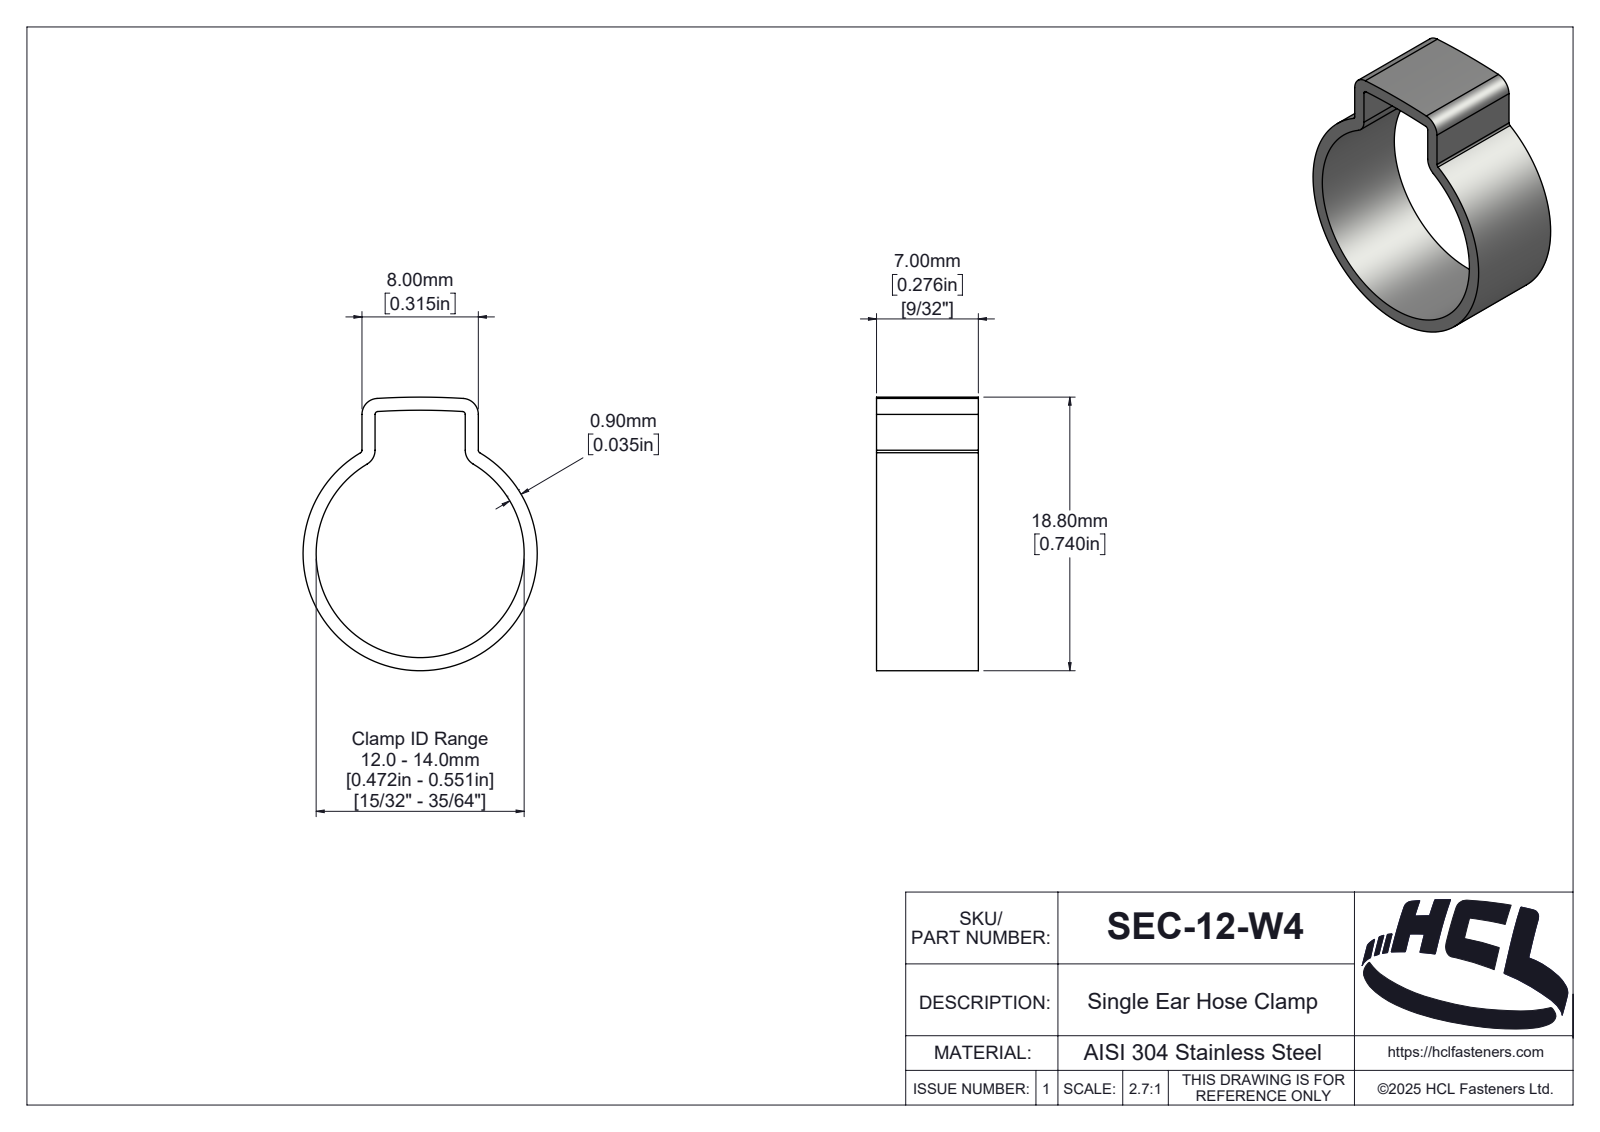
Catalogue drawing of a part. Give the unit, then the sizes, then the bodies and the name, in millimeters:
Units: millimetres
Overall size (bounding box): 18.8 × 16.1 × 7
Round holes (diameter × count): ⌀14.3 ×1
Round bosses / shafts (diameter × count): ⌀16.1 ×1
Partial cylindrical surfaces — rounded edges, fillets, slot ends (radius × count): R0.2 ×4, R1.1 ×4, R0.2 ×1, R0.81 ×1, R1.01 ×1, R1.06 ×1, R1.28 ×1, R1.81 ×1
Main face-to-face distances: 7, 0.9, 7.1, 8, 6.2, 3.73, 2.83, 3.37, 4.27, 3.88
Volume: 338 mm³ · Surface area: 853 mm²
Bodies: 1 solid, 123 faces (8 planar, 66 cylindrical, 49 other)
Part name (STEP PRODUCT): SEC-12-W4
STEP written by: SolidWorks 2025 (AUTOMOTIVE_DESIGN)
